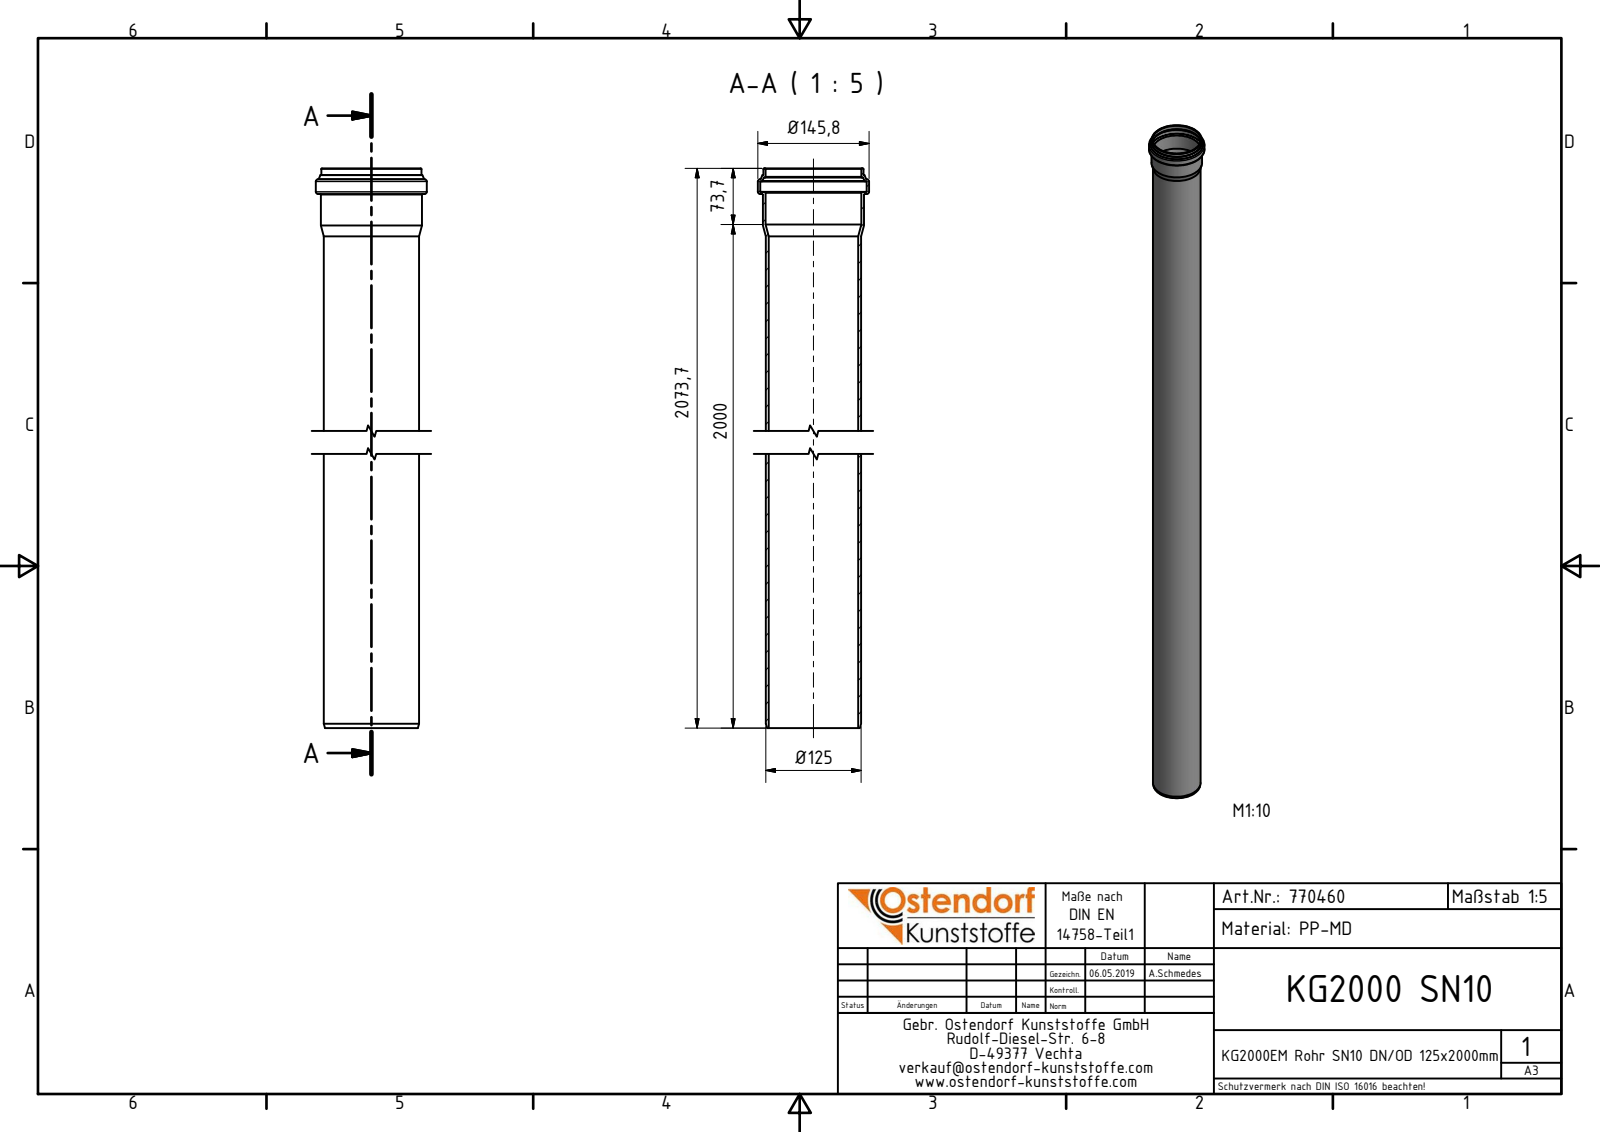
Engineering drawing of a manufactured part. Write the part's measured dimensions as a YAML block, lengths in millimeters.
part_name: "770460 KG2000EM Rohr SN10 DN-OD125x2000"
step_written_by: "Autodesk Inventor 2016 (AUTOMOTIVE_DESIGN)"
units: millimeters
bodies: {solids: 1, faces: 35, planar: 5, cylindrical: 8, other: 22}
overall_size: [2073.7, 145.8, 145.8]
volume: 3081000
surface_area: 1594000
round_holes:
  - {diameter: 117.2, count: 1}
  - {diameter: 125.5, count: 1}
  - {diameter: 139.8, count: 1}
round_bosses_or_shafts:
  - {diameter: 145.8, count: 1}
  - {diameter: 132.7, count: 1}
  - {diameter: 131.5, count: 1}
  - {diameter: 125, count: 1}
face_to_face_distances: [2040, 2073.7, 33.7, 2064.87, 24.87, 8.83, 2059.5, 19.5, 5.37, 14.2]
